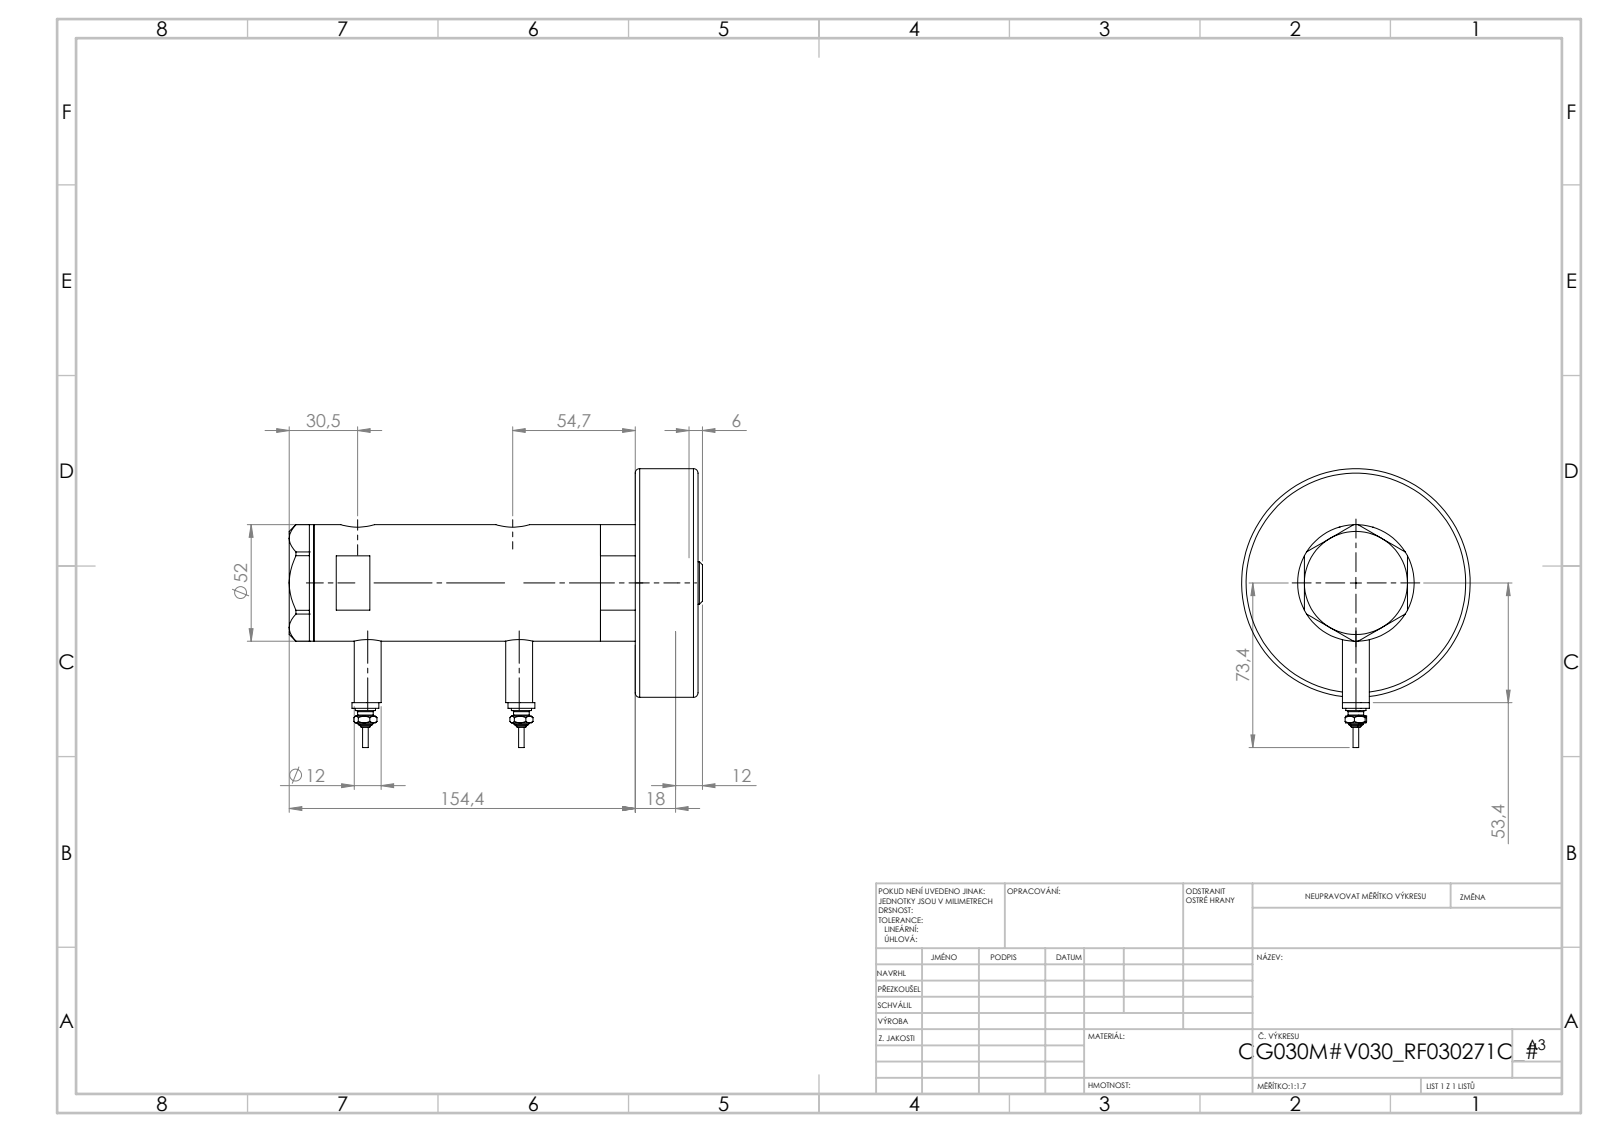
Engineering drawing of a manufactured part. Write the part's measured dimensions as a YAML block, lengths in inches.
part_name: "V270CG_271C; V270CG_SWITCH; V270CG_FRONT; V270CG_BACK (+2 more)"
step_written_by: "SolidWorks 2019 (CONFIG_CONTROL_DESIGN)"
units: inches
bodies: {solids: 7, faces: 256, planar: 97, cylindrical: 81, other: 78}
overall_size: [7.048, 4.303, 4.016]
volume: 31.45
surface_area: 158.7
round_holes:
  - {diameter: 0.197, count: 2}
  - {diameter: 0.383, count: 2}
  - {diameter: 0.492, count: 2}
  - {diameter: 0.591, count: 2}
  - {diameter: 0.256, count: 1}
  - {diameter: 0.787, count: 1}
  - {diameter: 0.846, count: 1}
  - {diameter: 1.181, count: 1}
  - {diameter: 1.299, count: 1}
  - {diameter: 1.575, count: 1}
  - {diameter: 1.732, count: 1}
round_bosses_or_shafts:
  - {diameter: 0.472, count: 3}
  - {diameter: 0.354, count: 2}
  - {diameter: 0.276, count: 2}
  - {diameter: 0.171, count: 2}
  - {diameter: 0.094, count: 2}
  - {diameter: 4.016, count: 1}
  - {diameter: 2.047, count: 1}
  - {diameter: 1.496, count: 1}
face_to_face_distances: [1.102, 5.333, 6.435, 0.937, 4.395, 5.498, 0.433, 1.37, 5.765, 6.868]
hole_center_spacings: [0.114, 0.177, 2.234, 2.348, 2.411, 2.526, 0.114, 0.115]
